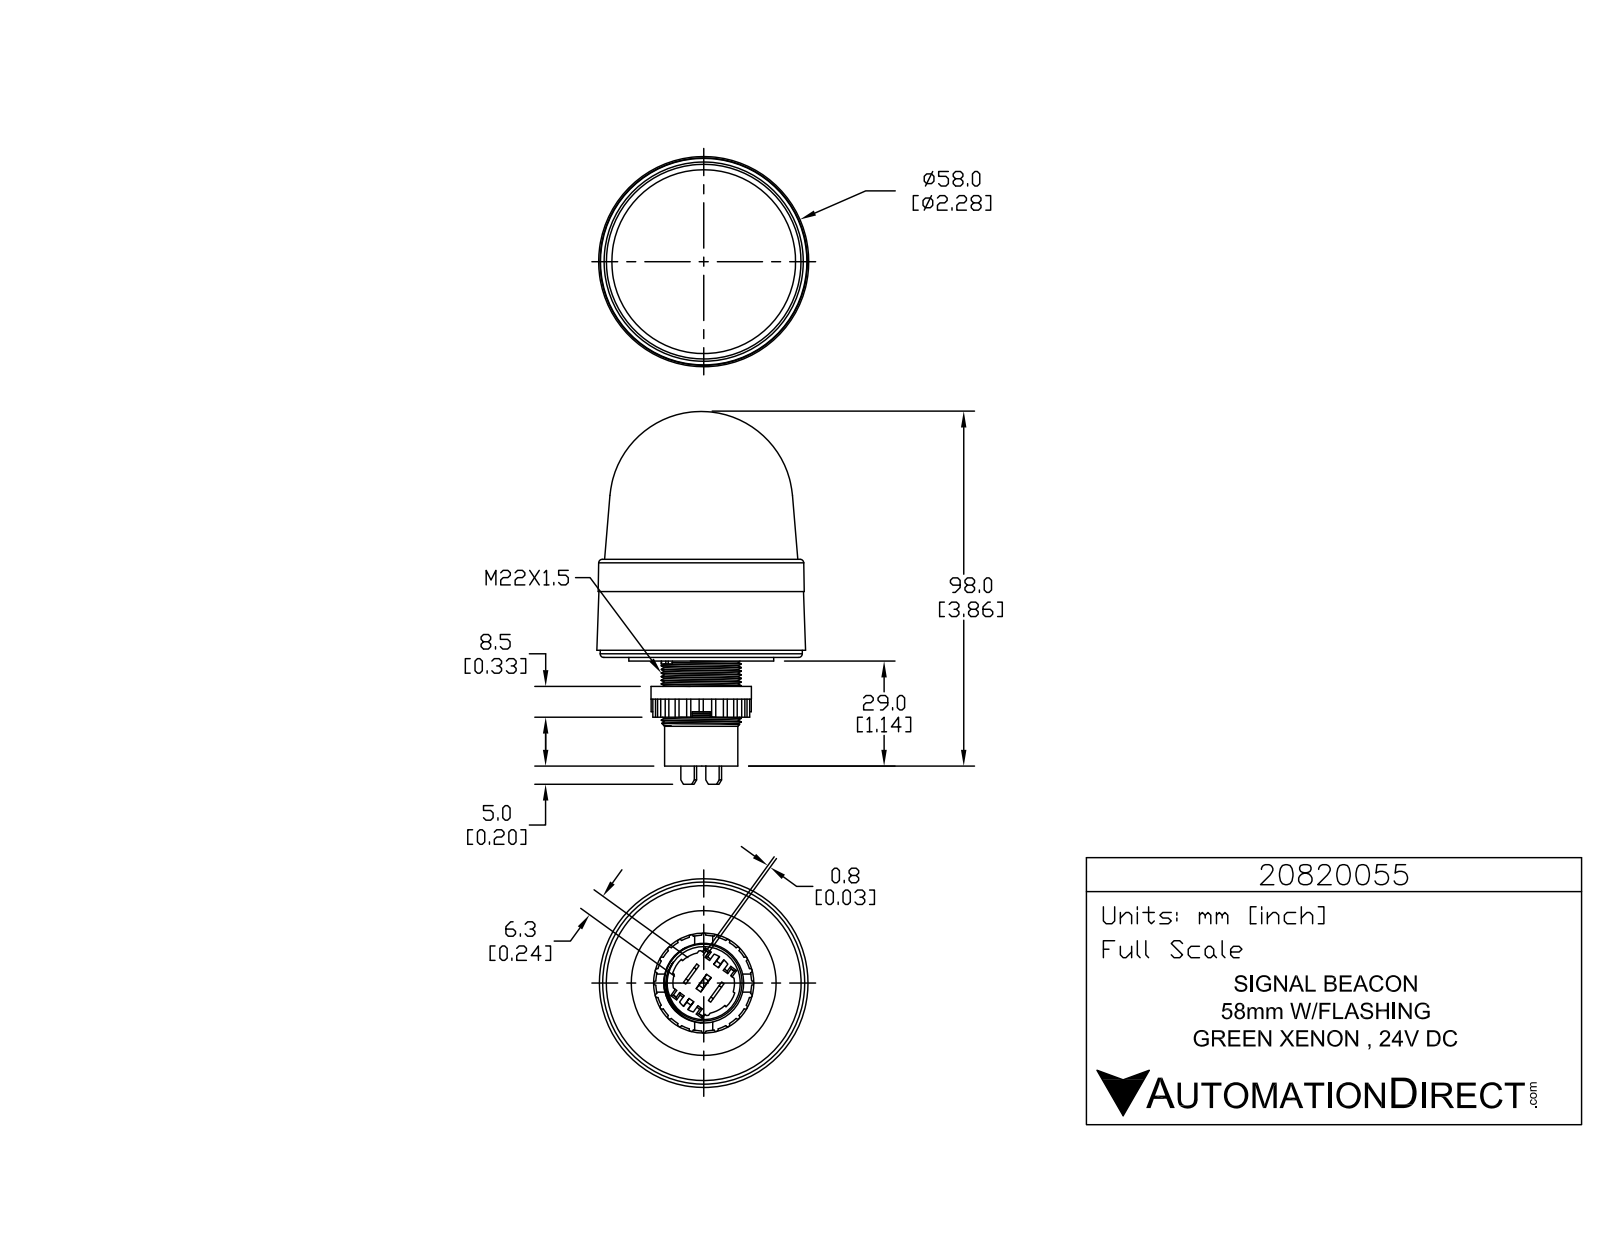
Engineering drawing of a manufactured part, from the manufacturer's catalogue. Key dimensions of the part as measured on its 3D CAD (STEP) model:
Part name (STEP PRODUCT): 20820055
STEP written by: SolidWorks 2015 (AUTOMOTIVE_DESIGN)
Units: inches
Bodies: 1 solid, 266 faces (119 planar, 120 cylindrical, 27 other)
Overall size (bounding box): 4.051 × 2.269 × 2.269
Volume: 9.016 in³ · Surface area: 31.05 in²
Round holes (diameter × count): ⌀0.906 ×1
Round bosses / shafts (diameter × count): ⌀2.197 ×1, ⌀1.575 ×1, ⌀1.091 ×1, ⌀0.866 ×1, ⌀0.795 ×1
Partial cylindrical surfaces — rounded edges, fillets, slot ends (radius × count): R0.023 ×24, R0.02 ×2, R0.335 ×1, R0.354 ×1, R0.522 ×1
Main face-to-face distances: 0.039, 0.276, 0.118, 1.142, 0.335, 0.315, 1.063, 0.748, 1.024, 0.728
